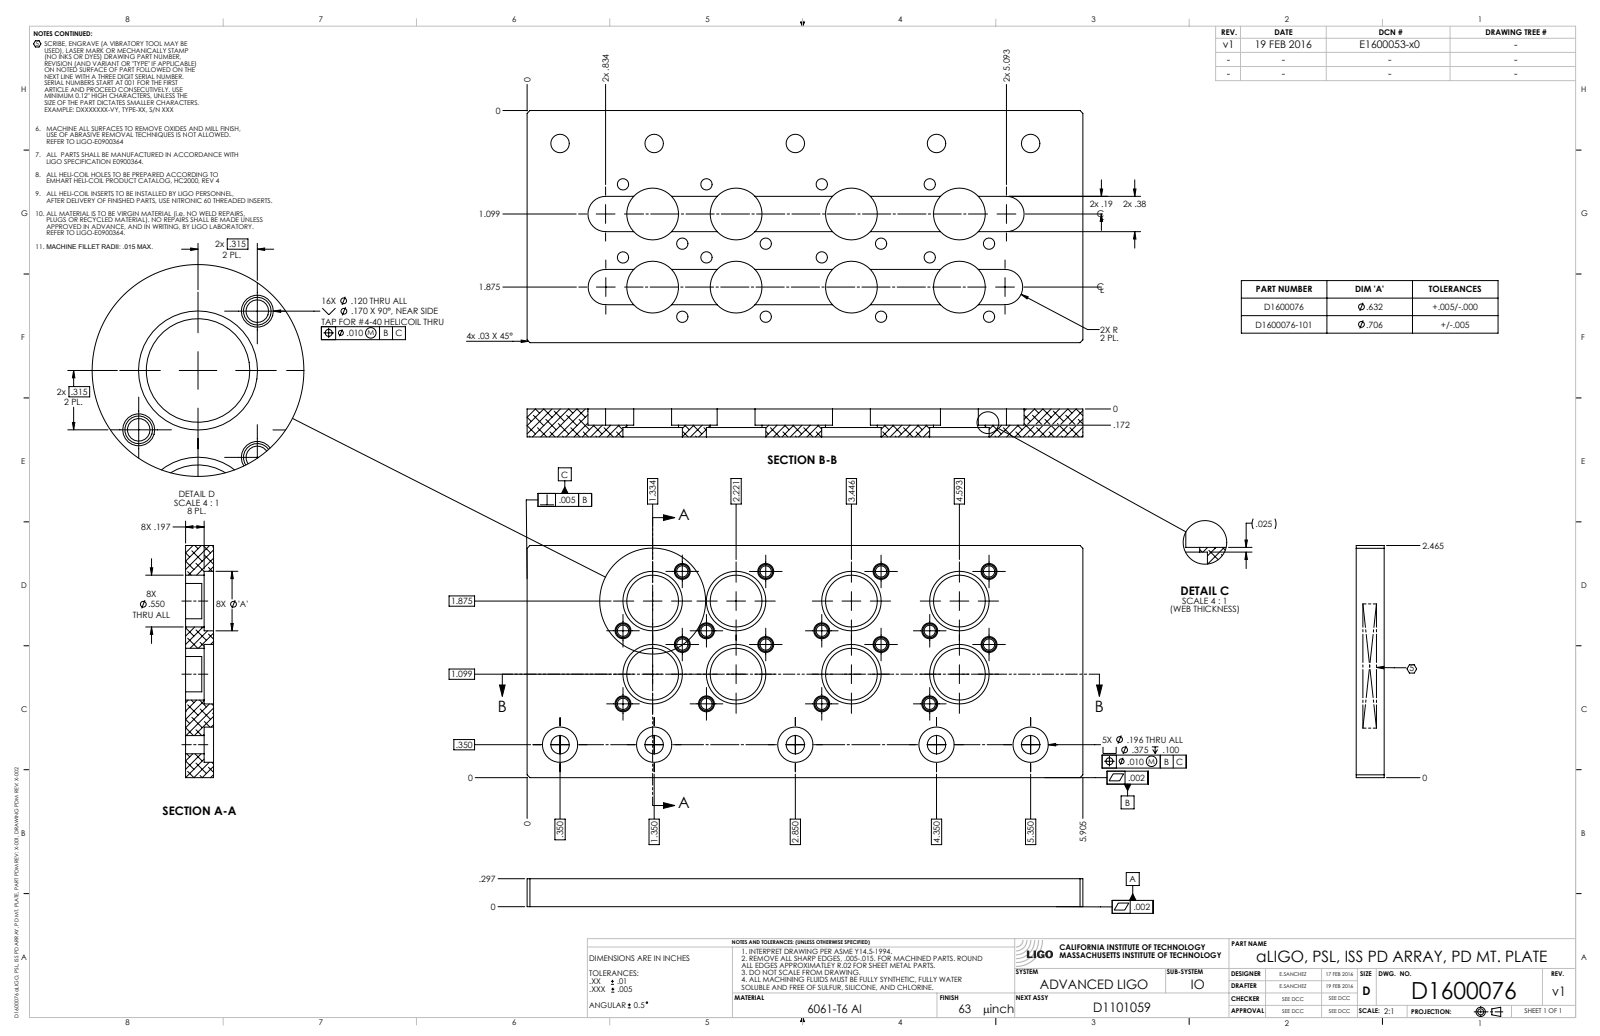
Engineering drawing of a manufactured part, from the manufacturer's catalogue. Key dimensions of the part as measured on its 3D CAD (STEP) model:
Part name (STEP PRODUCT): D1600076-v1
STEP written by: SolidWorks 2015 (AUTOMOTIVE_DESIGN)
Units: inches
Bodies: 1 solid, 223 faces (69 planar, 122 cylindrical, 32 other)
Overall size (bounding box): 5.905 × 2.465 × 0.297
Volume: 3.212 in³ · Surface area: 38.23 in²
Round holes (diameter × count): ⌀0.12 ×16, ⌀0.147 ×16, ⌀0.55 ×8, ⌀0.632 ×8, ⌀0.196 ×5, ⌀0.375 ×4, ⌀0.375 ×1
Partial cylindrical surfaces — rounded edges, fillets, slot ends (radius × count): R0.187 ×3, R0.188 ×1
Main face-to-face distances: 0.297, 0.172, 0.125, 2.465, 0.197, 0.025, 0.1, 5.905, 0.911, 1.554
Hole centre spacings: 0.445, 0.891, 0.776, 0.887, 2.372, 2.496, 3.259, 0.446
